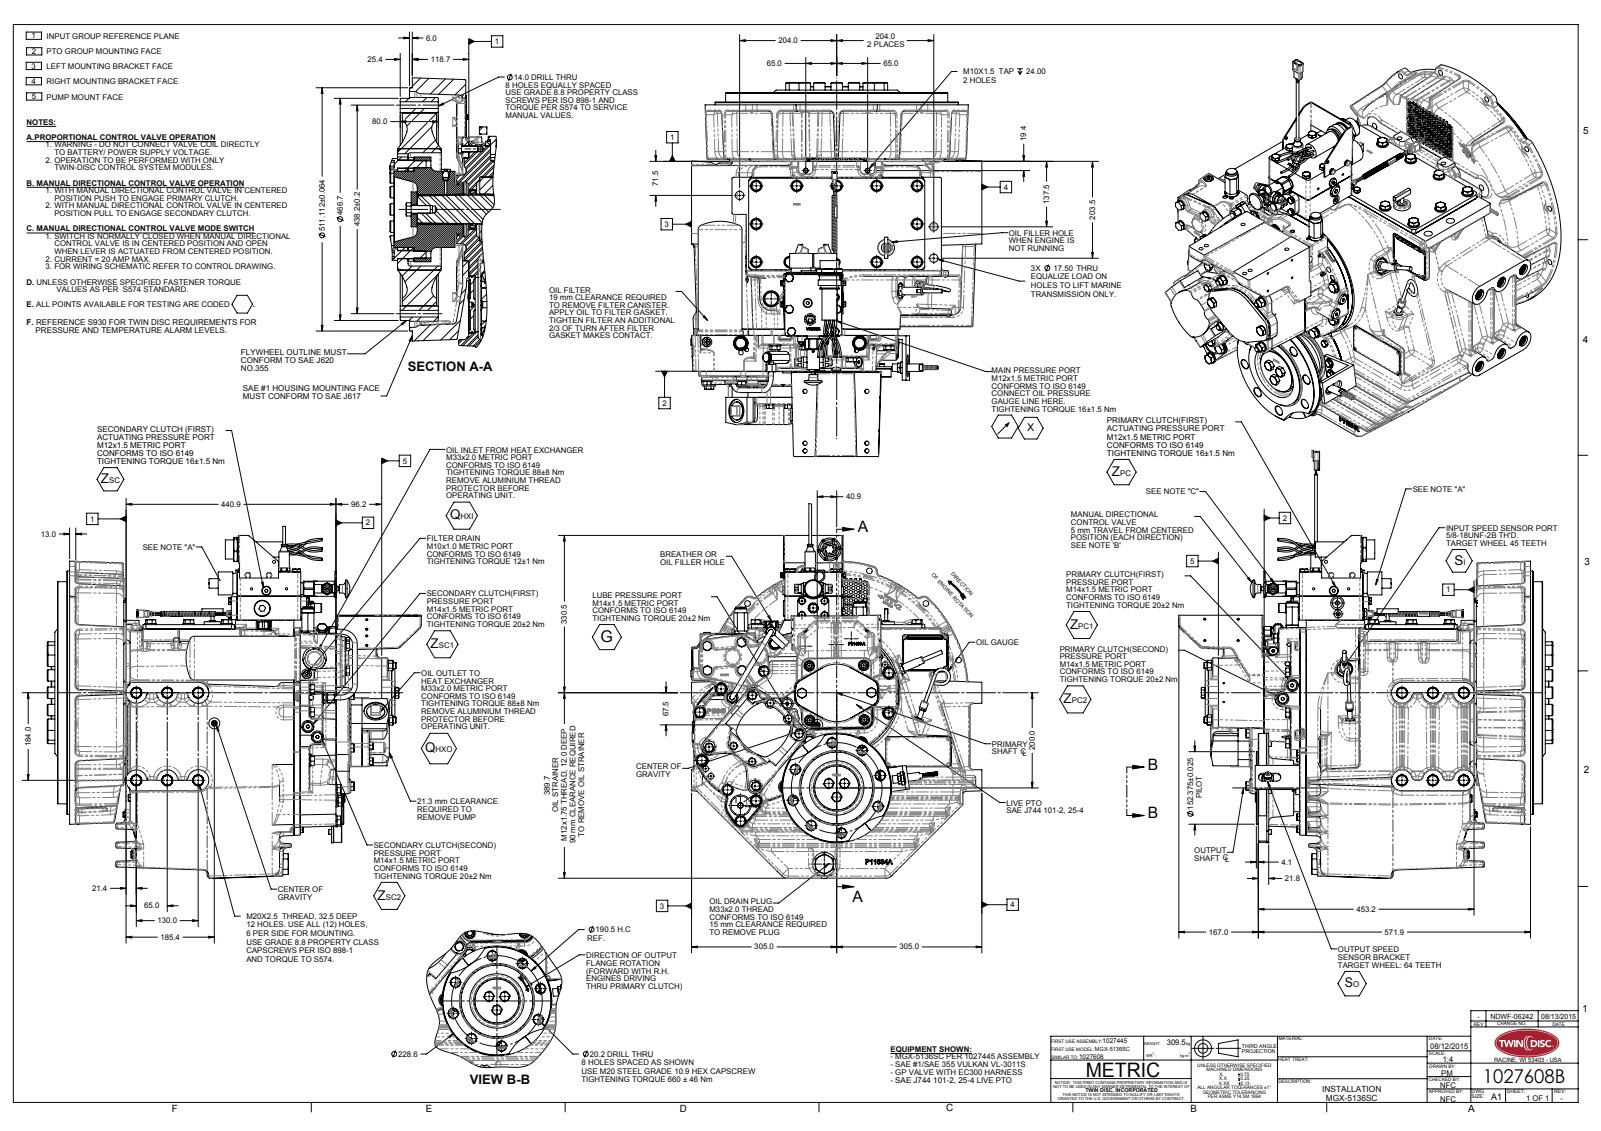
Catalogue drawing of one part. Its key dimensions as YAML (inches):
part_name: "1027608B"
step_written_by: "SolidWorks 2010 (AUTOMOTIVE_DESIGN)"
units: inches
bodies: {solids: 0, faces: 5593, planar: 1662, cylindrical: 1656, other: 2275}
overall_size: [35.411, 30.941, 24.113]
round_holes:
  - {diameter: 0.276, count: 86}
  - {diameter: 0.795, count: 14}
  - {diameter: 0.469, count: 12}
  - {diameter: 0.551, count: 9}
  - {diameter: 0.165, count: 8}
  - {diameter: 0.984, count: 8}
  - {diameter: 0.346, count: 6}
  - {diameter: 0.926, count: 5}
  - {diameter: 1.063, count: 5}
  - {diameter: 0.367, count: 4}
  - {diameter: 0.394, count: 4}
  - {diameter: 0.304, count: 3}
round_bosses_or_shafts:
  - {diameter: 0.945, count: 40}
  - {diameter: 0.394, count: 7}
  - {diameter: 0.744, count: 6}
  - {diameter: 0.11, count: 6}
  - {diameter: 0.472, count: 5}
  - {diameter: 0.1, count: 5}
  - {diameter: 0.781, count: 4}
  - {diameter: 0.74, count: 4}
partial_cylinders:
  - {radius: 0.118, count: 138}
  - {radius: 0.098, count: 81}
  - {radius: 0.315, count: 77}
  - {radius: 0.197, count: 60}
  - {radius: 0.256, count: 46}
  - {radius: 0.12, count: 25}
  - {radius: 0.63, count: 25}
  - {radius: 0.06, count: 18}
face_to_face_distances: [0.015, 0.515, 0.531, 0.031, 14.074, 14.059, 13.543, 14.599, 14.584, 14.069]
hole_center_spacings: [18.073, 5.401, 10.435, 14.756, 20.158, 0.787, 2.559, 5.402]
